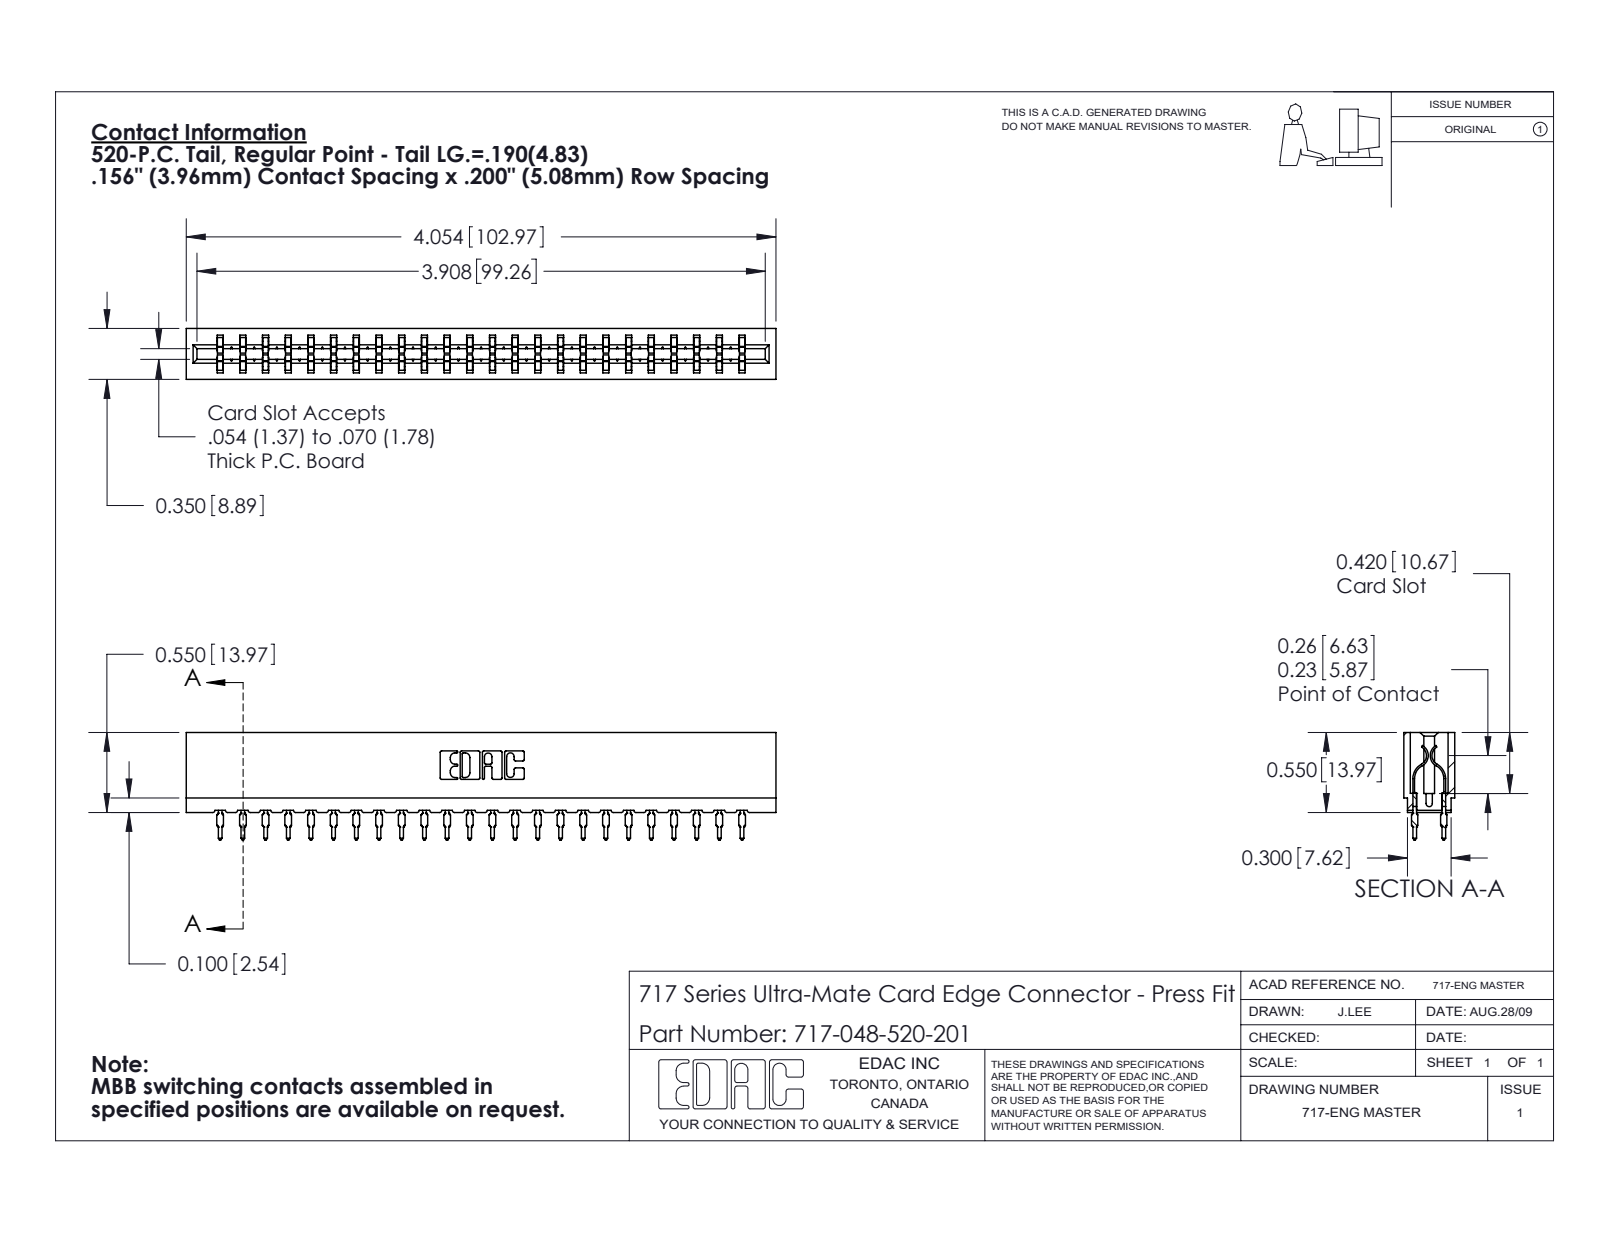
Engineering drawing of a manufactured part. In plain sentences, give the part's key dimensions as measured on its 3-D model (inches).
The part is named "745-292-001_520; 717-048-520-201; 717 Part_Insulator Option - 06". Its 3-D file was written by "SolidWorks 2020 (CONFIG_CONTROL_DESIGN)". It is 49 solids with 4414 faces: 2286 planar, 880 cylindrical and 1248 other. Overall it measures 4.054 by 0.739 by 0.35 inches. Its volume is 0.547 cubic inches and its surface area 20.48 square inches. Partial cylindrical surfaces (rounded edges, fillets, slot ends): 96 of radius 0.021, 48 of radius 0.015, 22 of radius 0.01, 8 of radius 0.005, 8 of radius 0.011, 6 of radius 0.007, 6 of radius 0.031, 3 of radius 0.026. The main face-to-face distances are 0.212, 0.138, 0.35, 0.156, 0.063, 0.287, 0.076, 0.149, 0.074, 0.624.
